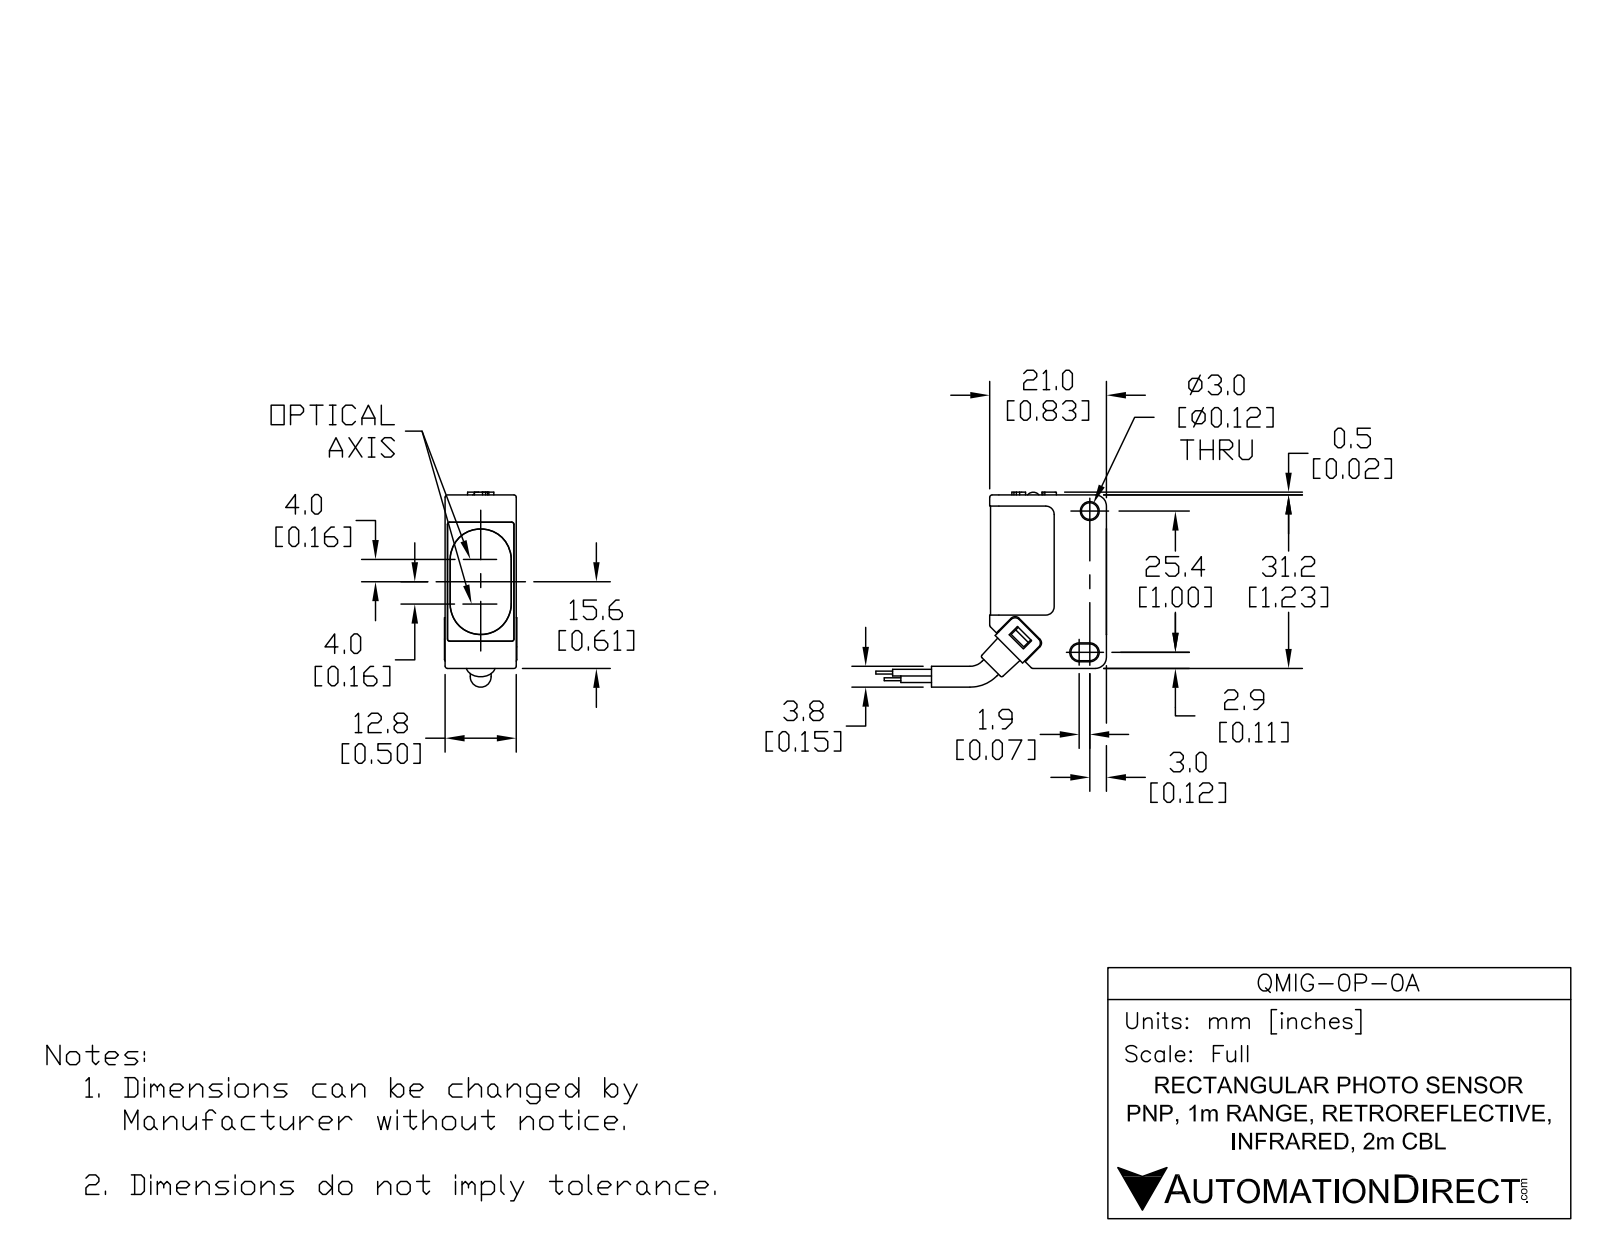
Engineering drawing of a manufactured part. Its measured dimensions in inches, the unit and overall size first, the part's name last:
Units: inches
Overall size (bounding box): 3.193 × 1.032 × 0.512
Round holes (diameter × count): ⌀0.118 ×3, ⌀0.148 ×1, ⌀0.224 ×1, ⌀0.283 ×1
Round bosses / shafts (diameter × count): ⌀0.138 ×2
Partial cylindrical surfaces — rounded edges, fillets, slot ends (radius × count): R0.016 ×13, R0.02 ×10, R0.039 ×8, R0.059 ×6, R0.024 ×4, R0.006 ×2, R0.035 ×2, R0.044 ×2
Main face-to-face distances: 0.02, 0.498, 0.059, 0.016, 0.504, 0.138, 0.488, 0.079, 0.482, 0.492
Hole centre spacings: 0.205
Volume: 0.47 in³ · Surface area: 8.375 in²
Bodies: 9 solids, 258 faces (134 planar, 100 cylindrical, 24 other)
Part name (STEP PRODUCT): QMIG-0P-0A
STEP written by: SolidWorks 2017 (AUTOMOTIVE_DESIGN)
